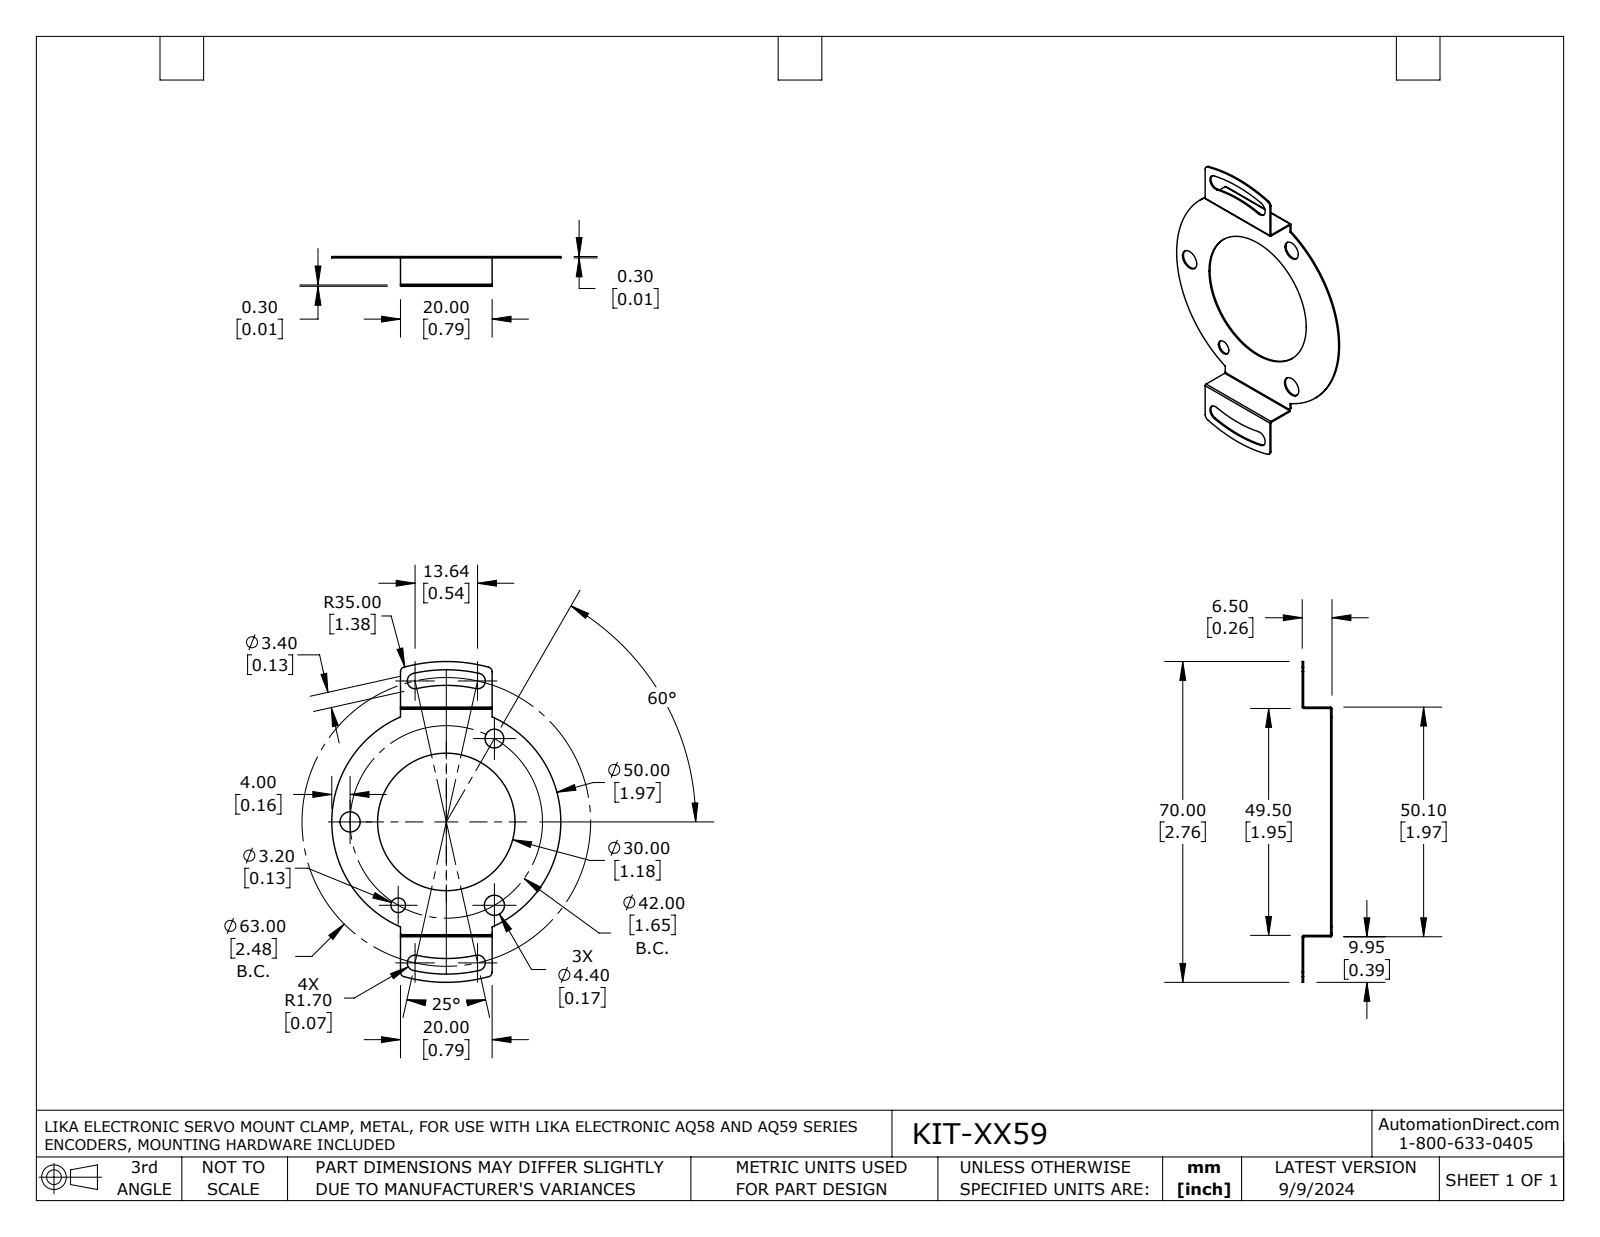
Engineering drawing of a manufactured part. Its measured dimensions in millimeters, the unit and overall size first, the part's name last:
Units: millimetres
Overall size (bounding box): 70 × 50 × 6.5
Round holes (diameter × count): ⌀4.4 ×2, ⌀3.2 ×1, ⌀4.1 ×1, ⌀30 ×1
Partial cylindrical surfaces — rounded edges, fillets, slot ends (radius × count): R0.2 ×4, R0.3 ×4, R1 ×4, R1.7 ×4, R25 ×1, R29.8 ×1, R33.2 ×1, R35 ×1
Main face-to-face distances: 6.2, 6.5, 5.9, 49.8, 50.1, 49.5, 20, 13.2
Hole centre spacings: 21, 36.4, 36.4, 42
Volume: 520 mm³ · Surface area: 3 615 mm²
Bodies: 1 solid, 60 faces (22 planar, 38 cylindrical, 0 other)
Part name (STEP PRODUCT): KIT-XX59
STEP written by: SolidWorks 2021 (AUTOMOTIVE_DESIGN)
